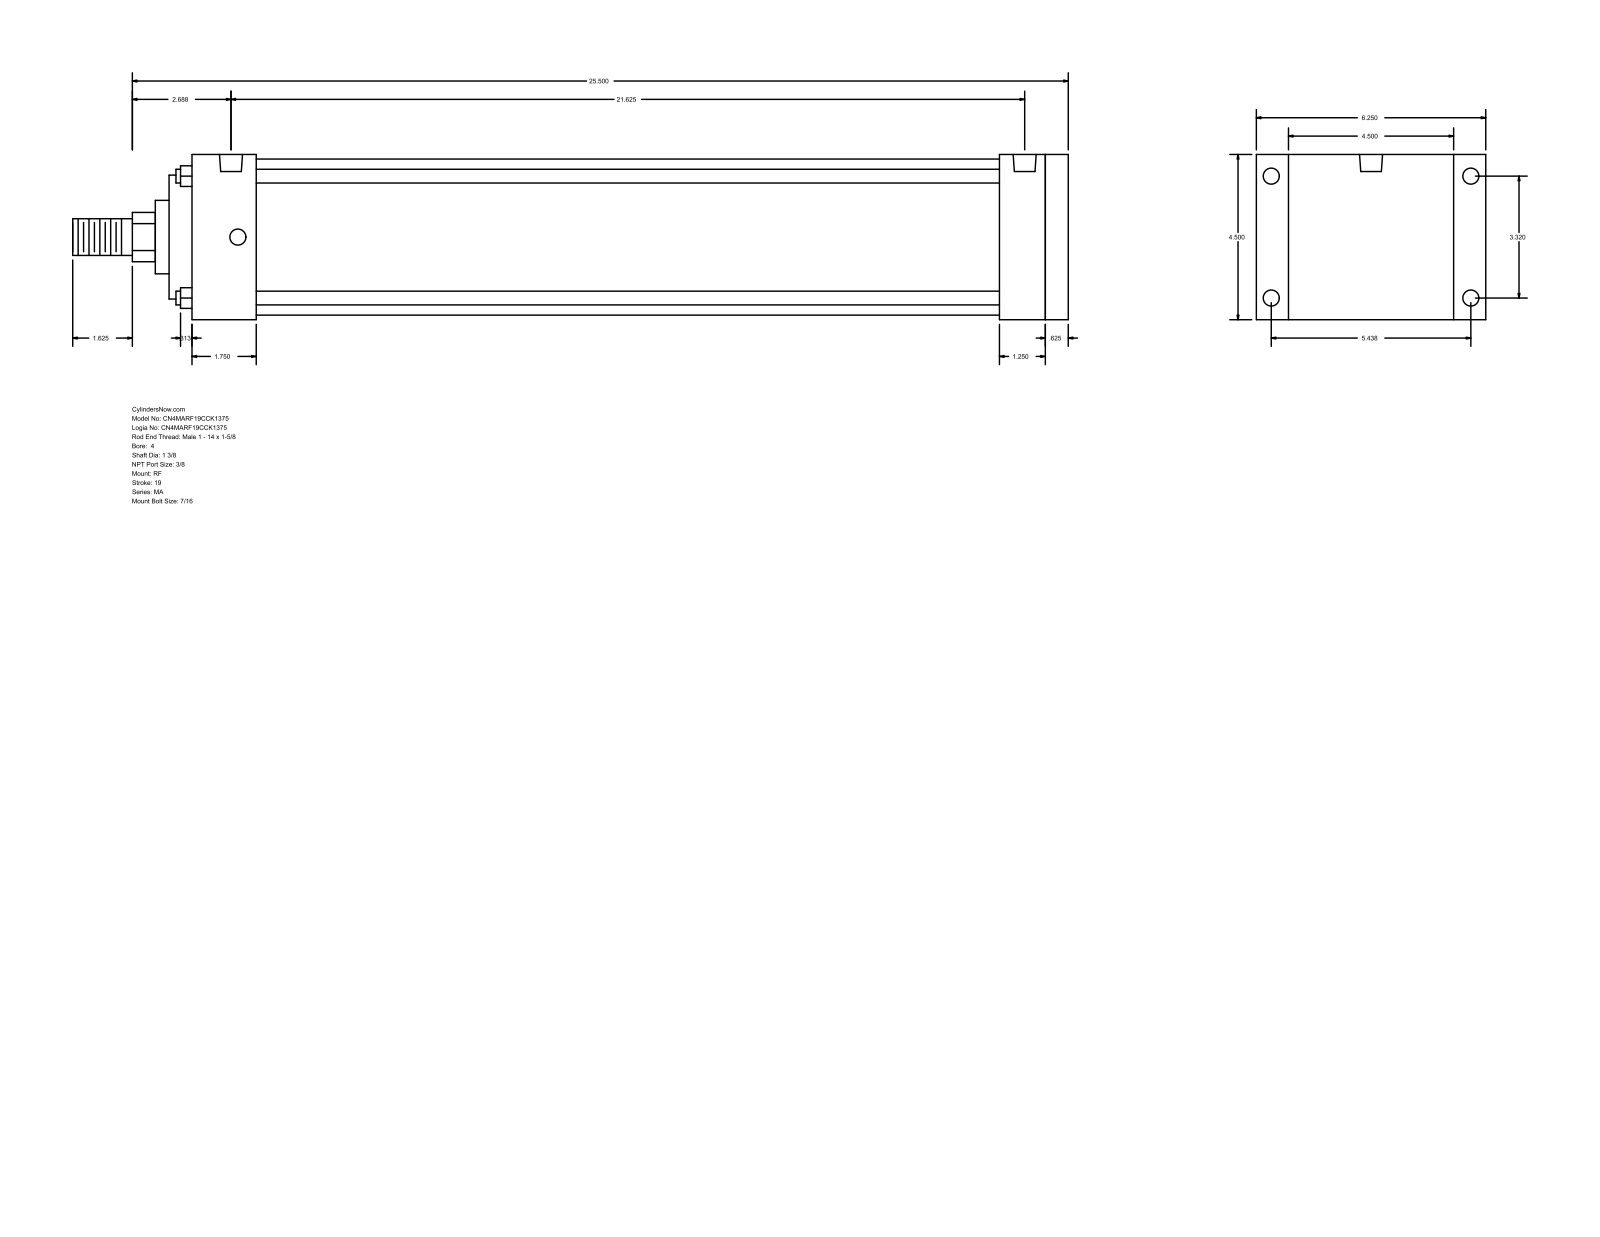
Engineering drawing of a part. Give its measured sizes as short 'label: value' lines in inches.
name: MA_RF__0400_1.375
written by: GSSL Pune (CONFIG_CONTROL_DESIGN)
unit: in
bodies: 0 solids, 94 faces (65 planar, 29 cylindrical, 0 other)
size: 27.125 × 6.25 × 4.5
holes: 8× ⌀0.437, 2× ⌀0.627
bosses: 4× ⌀0.375, 1× ⌀4.25, 1× ⌀3.375, 1× ⌀2, 1× ⌀1.375, 1× ⌀1
rounds: 1× R0.672
face distances: 4.5, 23.875, 0.625, 23.25, 24.5, 0.875, 5.375, 22.625, 22, 1.25
hole spacings: 0.188, 3.32, 5.438, 6.371, 21.25, 21.437, 21.625
